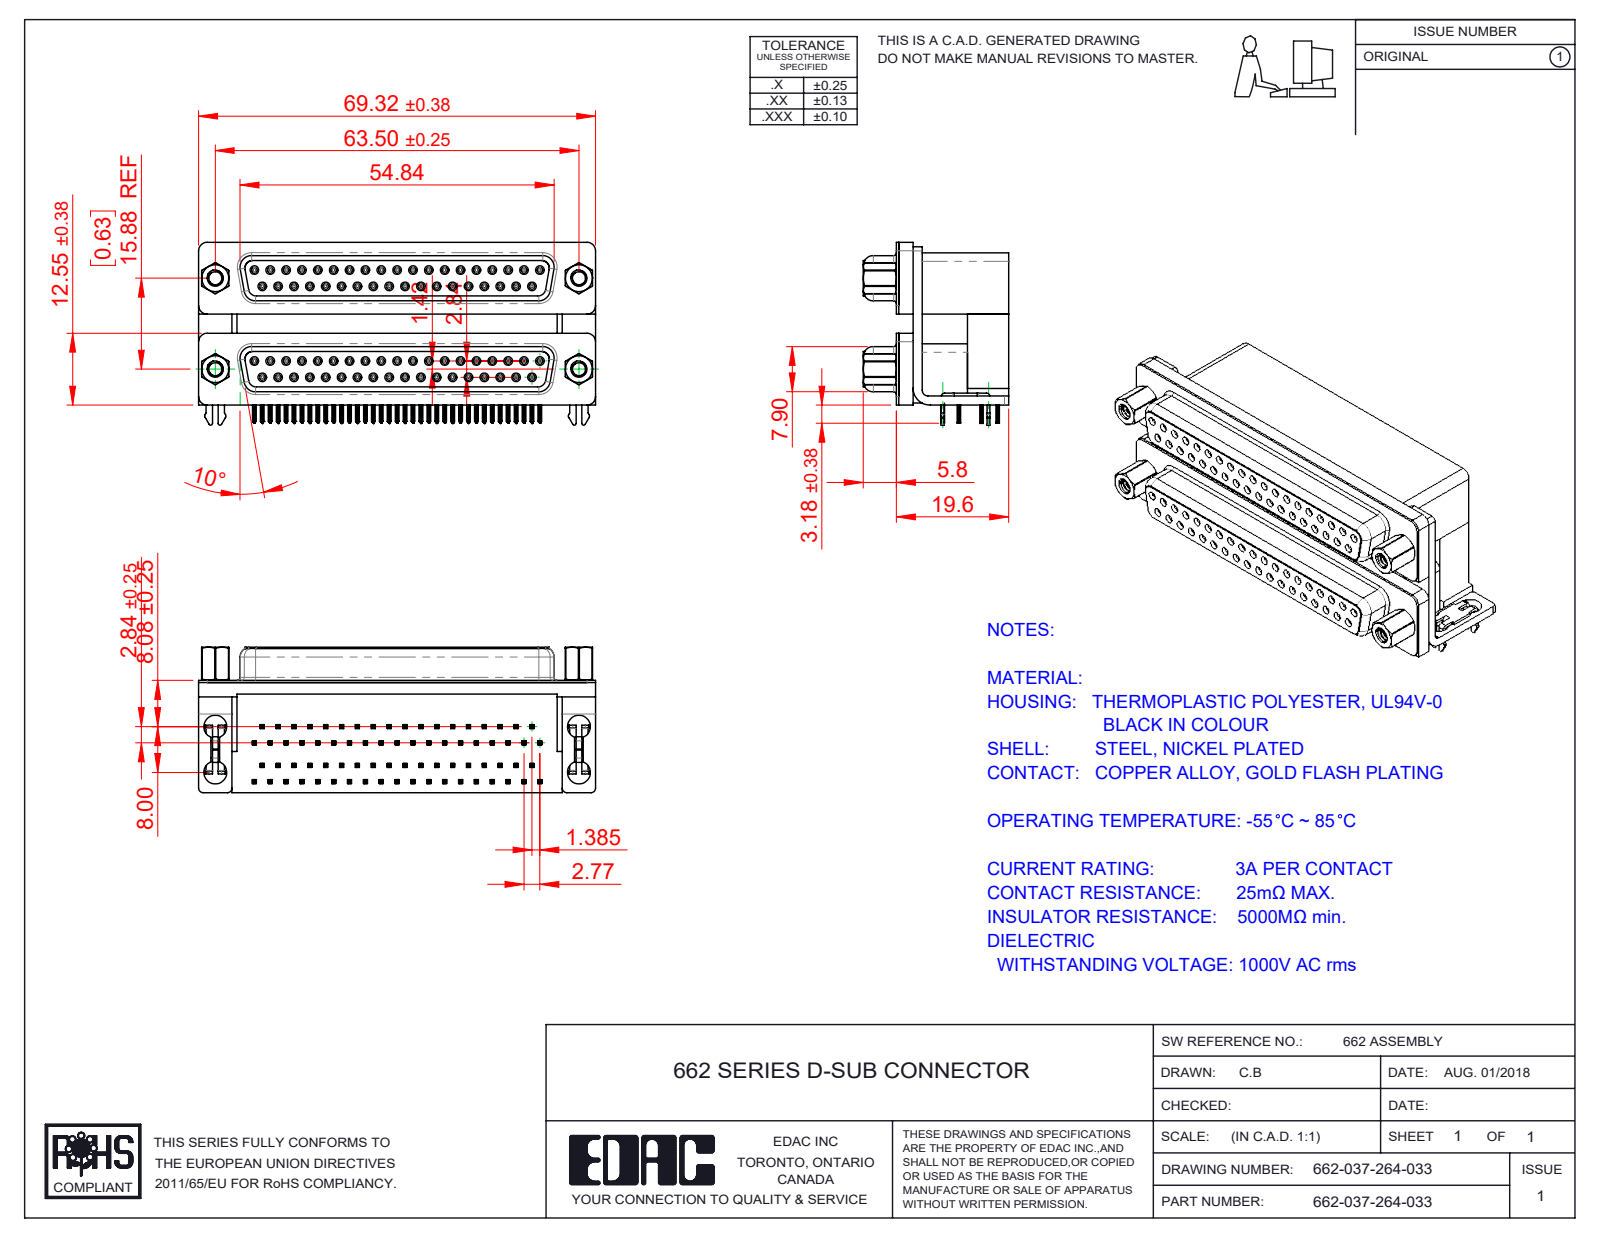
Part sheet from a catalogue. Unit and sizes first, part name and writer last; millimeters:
Units: millimetres
Overall size (bounding box): 69.32 × 31.93 × 25.4
Round holes (diameter × count): ⌀0.8 ×74, ⌀0.9 ×74, ⌀4 ×8, ⌀2.26 ×4, ⌀2.29 ×4, ⌀3.5 ×4, ⌀4.8 ×4, ⌀5 ×4
Round bosses / shafts (diameter × count): ⌀1.2 ×74, ⌀4.9 ×4, ⌀4.75 ×4, ⌀3.9 ×4, ⌀2.79 ×4
Partial cylindrical surfaces — rounded edges, fillets, slot ends (radius × count): R0.1 ×594, R0.15 ×296, R0.35 ×148, R0.34 ×74, R0.28 ×36, R1.35 ×18, R0.5 ×12, R1.5 ×12
Main face-to-face distances: 0.4, 19.2, 15.88, 6.2, 7.2, 12, 15.52, 2.84, 26.22, 10.7
Hole centre spacings: 3.16, 2.77, 5.54, 8.31, 11.08, 22.16, 13.85, 19.39
Volume: 32 200 mm³ · Surface area: 35 294 mm²
Bodies: 91 solids, 11712 faces (5378 planar, 2754 cylindrical, 3580 other)
Part name (STEP PRODUCT): 662 Contact Bottom Upper_L; 662 4-40 Hex Standoff 5; 662 Contact Bottom Lower; 662 Housing Spacer_37 Contacts L (+8 more)
STEP written by: SolidWorks 2020 (CONFIG_CONTROL_DESIGN)
